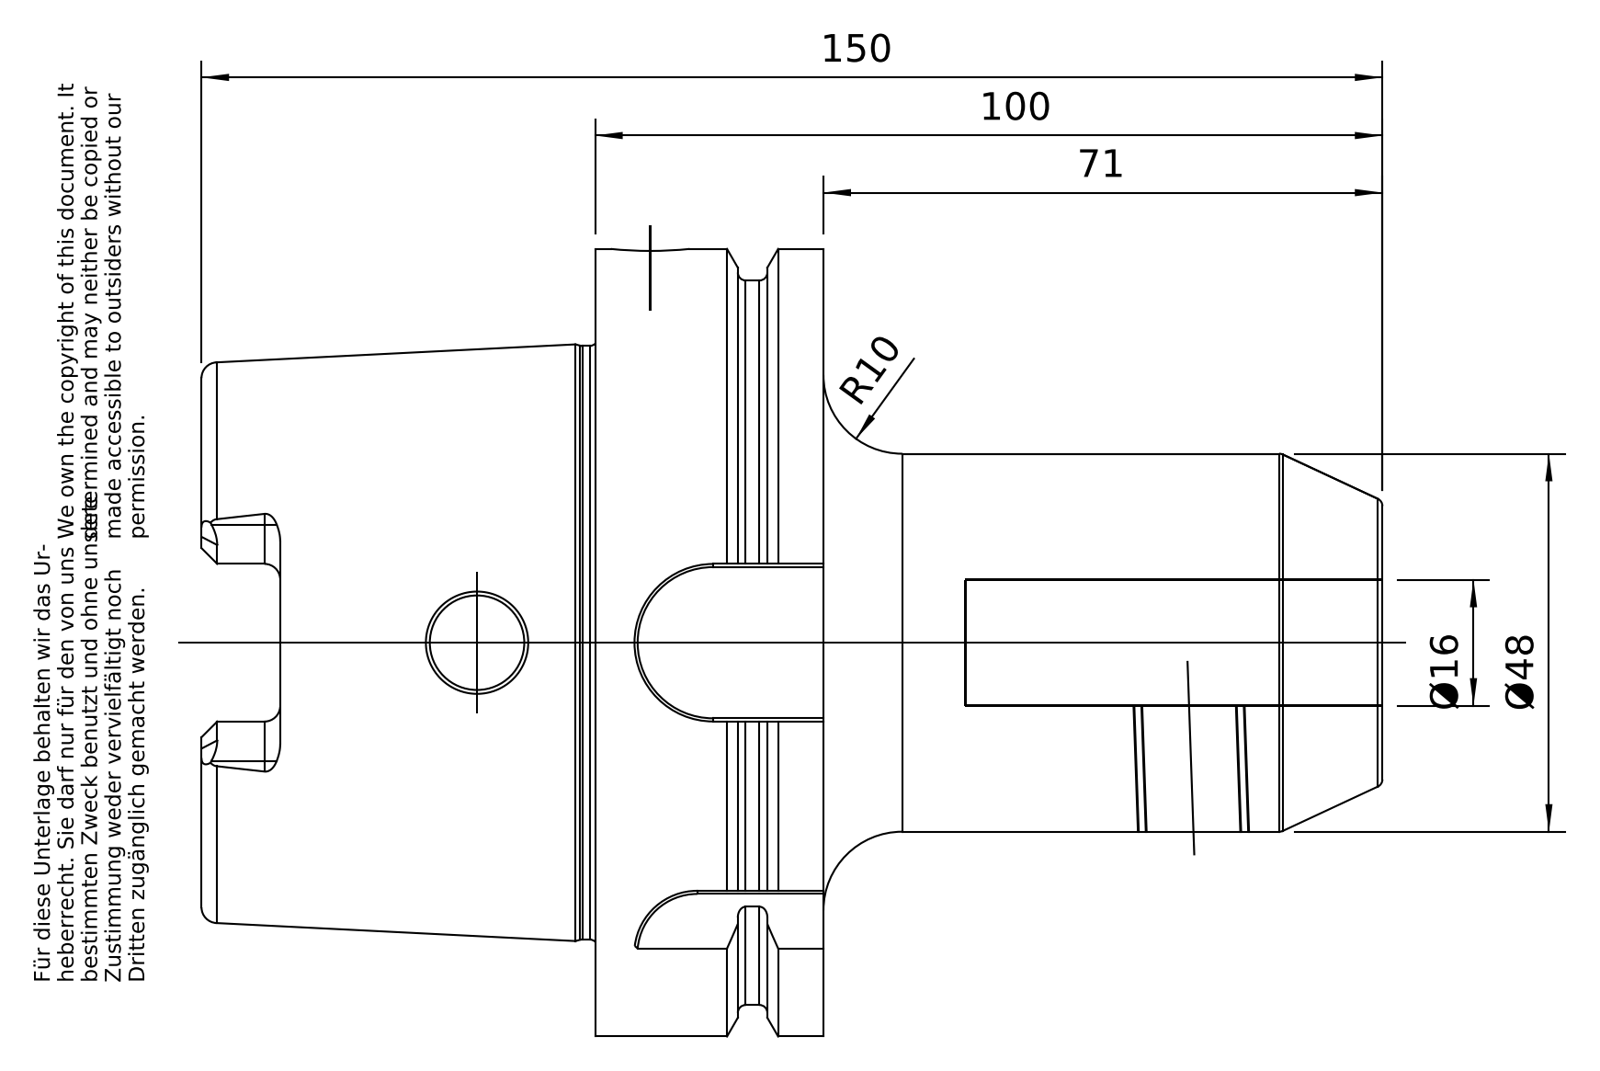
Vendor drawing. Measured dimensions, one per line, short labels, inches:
name: A100-030-16
written by: PRO/ENGINEER BY PARAMETRIC TECHNOLOGY CORPORATION, 2010430 (CONFIG_CONTROL_DESIGN)
unit: in
bodies: 1 solid, 180 faces (50 planar, 55 cylindrical, 75 other)
size: 5.906 × 3.937 × 3.937
volume: 22.53 in³; area: 97.73 in²
holes: 1× ⌀0.394, 1× ⌀0.472, 1× ⌀0.492, 1× ⌀0.551, 1× ⌀0.63, 1× ⌀0.886, 1× ⌀0.945, 1× ⌀0.957, 1× ⌀0.965, 1× ⌀2.087, 1× ⌀2.48
bosses: 1× ⌀3.937, 1× ⌀3.622, 1× ⌀2.967, 1× ⌀1.89
rounds: 6× R0.079, 4× R0.197, 1× R0.315, 1× R0.394, 1× R0.433
face distances: 1.142, 0.492, 0.65, 1.969, 2.461, 3.11, 5.906, 3.937, 3.445, 2.795
